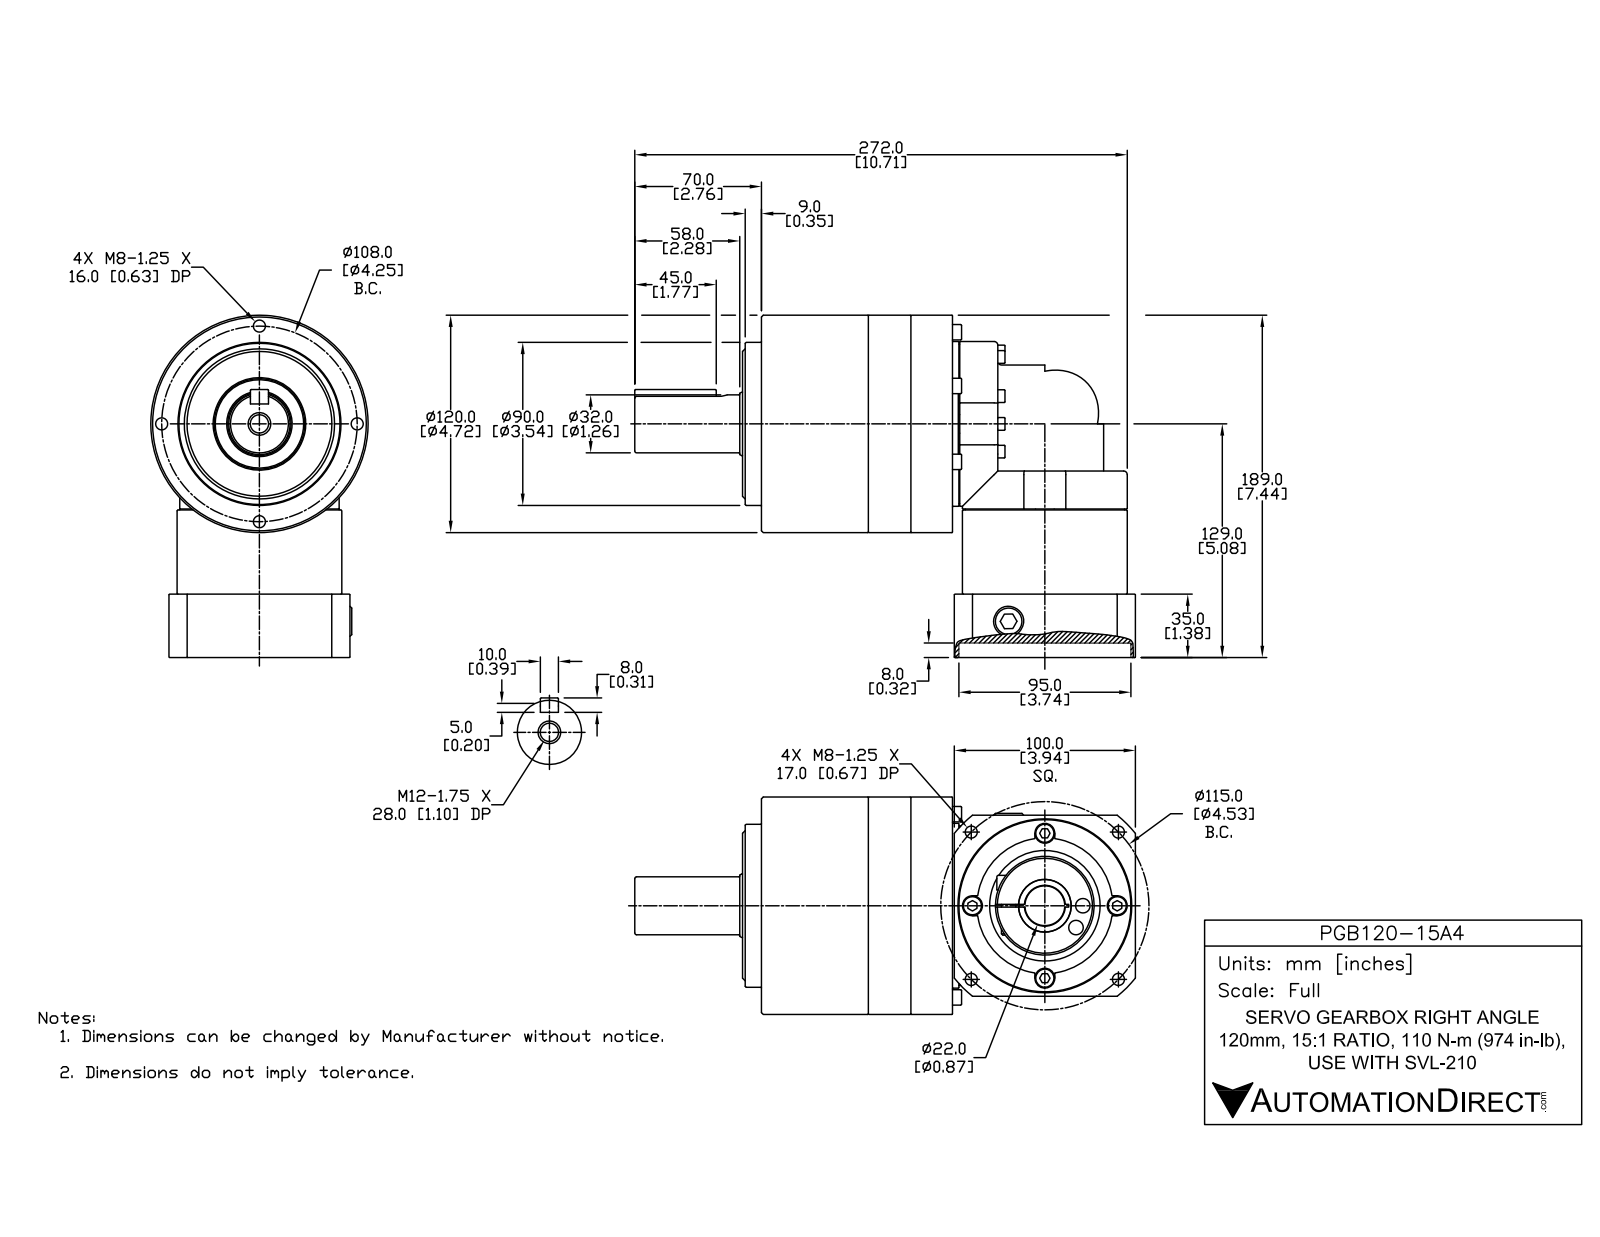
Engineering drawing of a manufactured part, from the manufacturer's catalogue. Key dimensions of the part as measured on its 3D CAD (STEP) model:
Part name (STEP PRODUCT): PGB120-15A4
STEP written by: SolidWorks 2014 (AUTOMOTIVE_DESIGN)
Units: inches
Bodies: 1 solid, 640 faces (271 planar, 166 cylindrical, 203 other)
Overall size (bounding box): 10.886 × 7.441 × 4.724
Volume: 137.2 in³ · Surface area: 249.4 in²
Round holes (diameter × count): ⌀0.262 ×8, ⌀0.217 ×6, ⌀0.433 ×4, ⌀0.315 ×2, ⌀0.346 ×1, ⌀0.398 ×1, ⌀0.561 ×1, ⌀0.866 ×1, ⌀2.402 ×1, ⌀2.953 ×1, ⌀3.74 ×1
Round bosses / shafts (diameter × count): ⌀0.276 ×9, ⌀0.335 ×6, ⌀0.197 ×6, ⌀0.394 ×4, ⌀3.583 ×2, ⌀3.465 ×2, ⌀4.724 ×1, ⌀3.543 ×1
Partial cylindrical surfaces — rounded edges, fillets, slot ends (radius × count): R0.079 ×6, R1.28 ×2, R0.131 ×1, R0.197 ×1, R0.276 ×1, R2.52 ×1
Main face-to-face distances: 3.937, 4.154, 0.413, 4.567, 0.039, 4.606, 3.976, 8.13, 8.543, 4.193
Hole centre spacings: 1.601, 3.556, 0.836, 2.156, 2.379, 3.56, 4.199, 1.65
